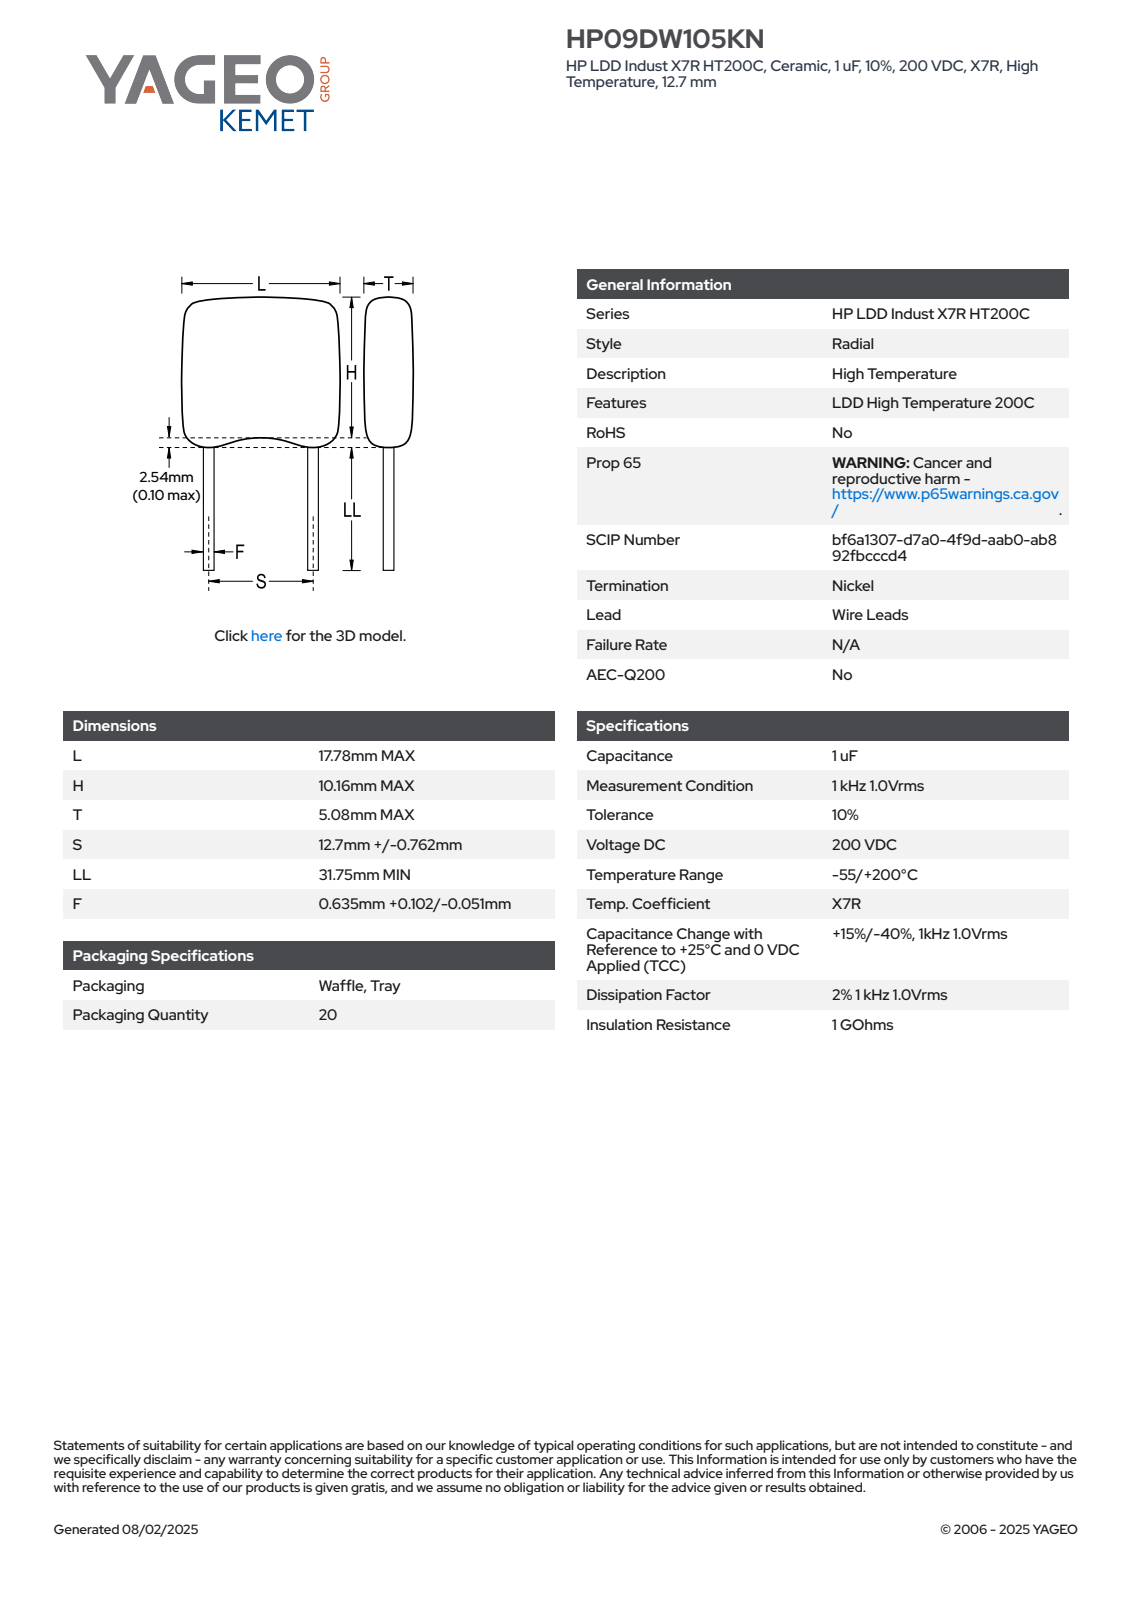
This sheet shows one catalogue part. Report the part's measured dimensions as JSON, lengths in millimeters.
{"part_name": "CCR_RMSTHP_HP09_L17.78H10.16T5.08S12.7LL3.175F0.737", "step_written_by": "SolidWorks 2014 (AUTOMOTIVE_DESIGN)", "units": "millimeters", "bodies": {"solids": 4, "faces": 83, "planar": 65, "cylindrical": 14, "other": 4}, "overall_size": [17.78, 14.86, 5.08], "volume_mm3": 1043, "surface_area_mm2": 714, "round_bosses_or_shafts": [[0.74, 2]], "partial_cylinders_radius": [[0.75, 10]], "face_to_face_distances": [5.08, 11.68, 17.78, 3.18, 14.86, 9.76, 6.58, 5.1, 7.64, 4.46]}
